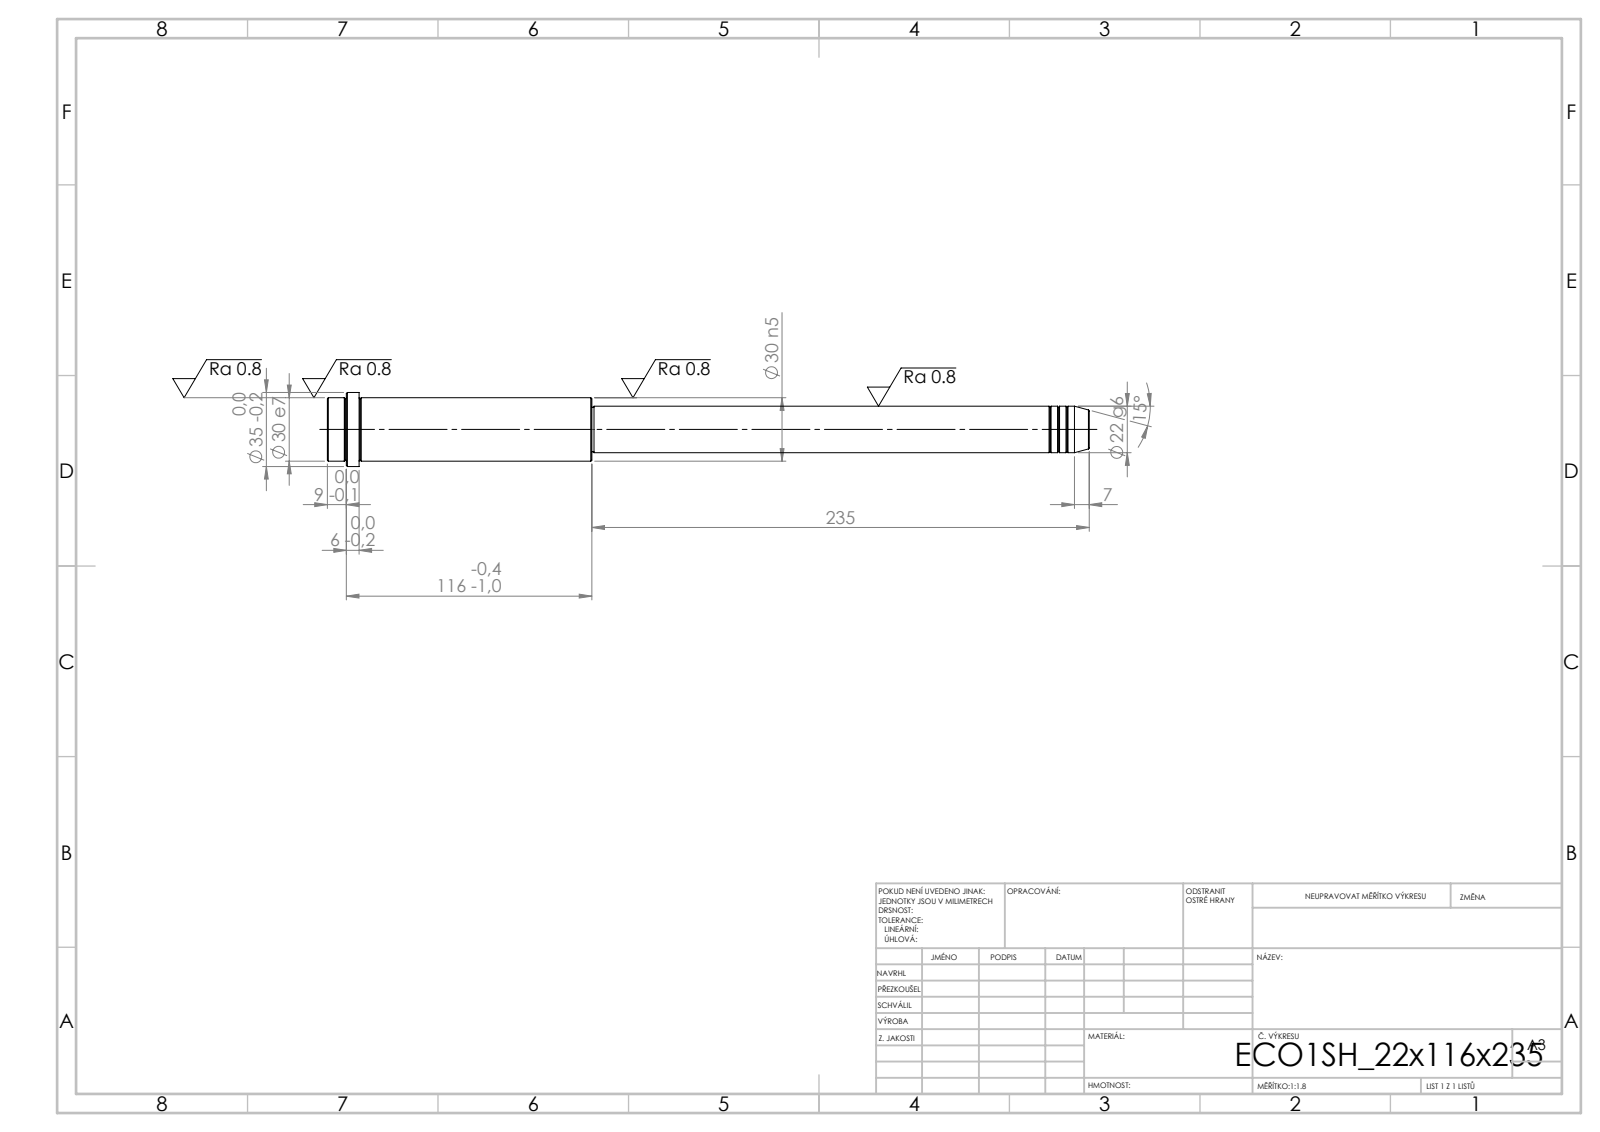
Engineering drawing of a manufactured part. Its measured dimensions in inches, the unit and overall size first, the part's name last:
Units: inches
Overall size (bounding box): 14.173 × 1.378 × 1.378
Round bosses / shafts (diameter × count): ⌀1.378 ×1, ⌀1.181 ×1, ⌀0.866 ×1, ⌀0.827 ×1
Main face-to-face distances: 4.921, 4.331, 0.591, 9.252, 13.583, 14.173, 13.819, 4.567, 0.236, 0.354
Volume: 10.9 in³ · Surface area: 46.62 in²
Bodies: 1 solid, 52 faces (6 planar, 16 cylindrical, 30 other)
STEP written by: SolidWorks 2019 (CONFIG_CONTROL_DESIGN)
